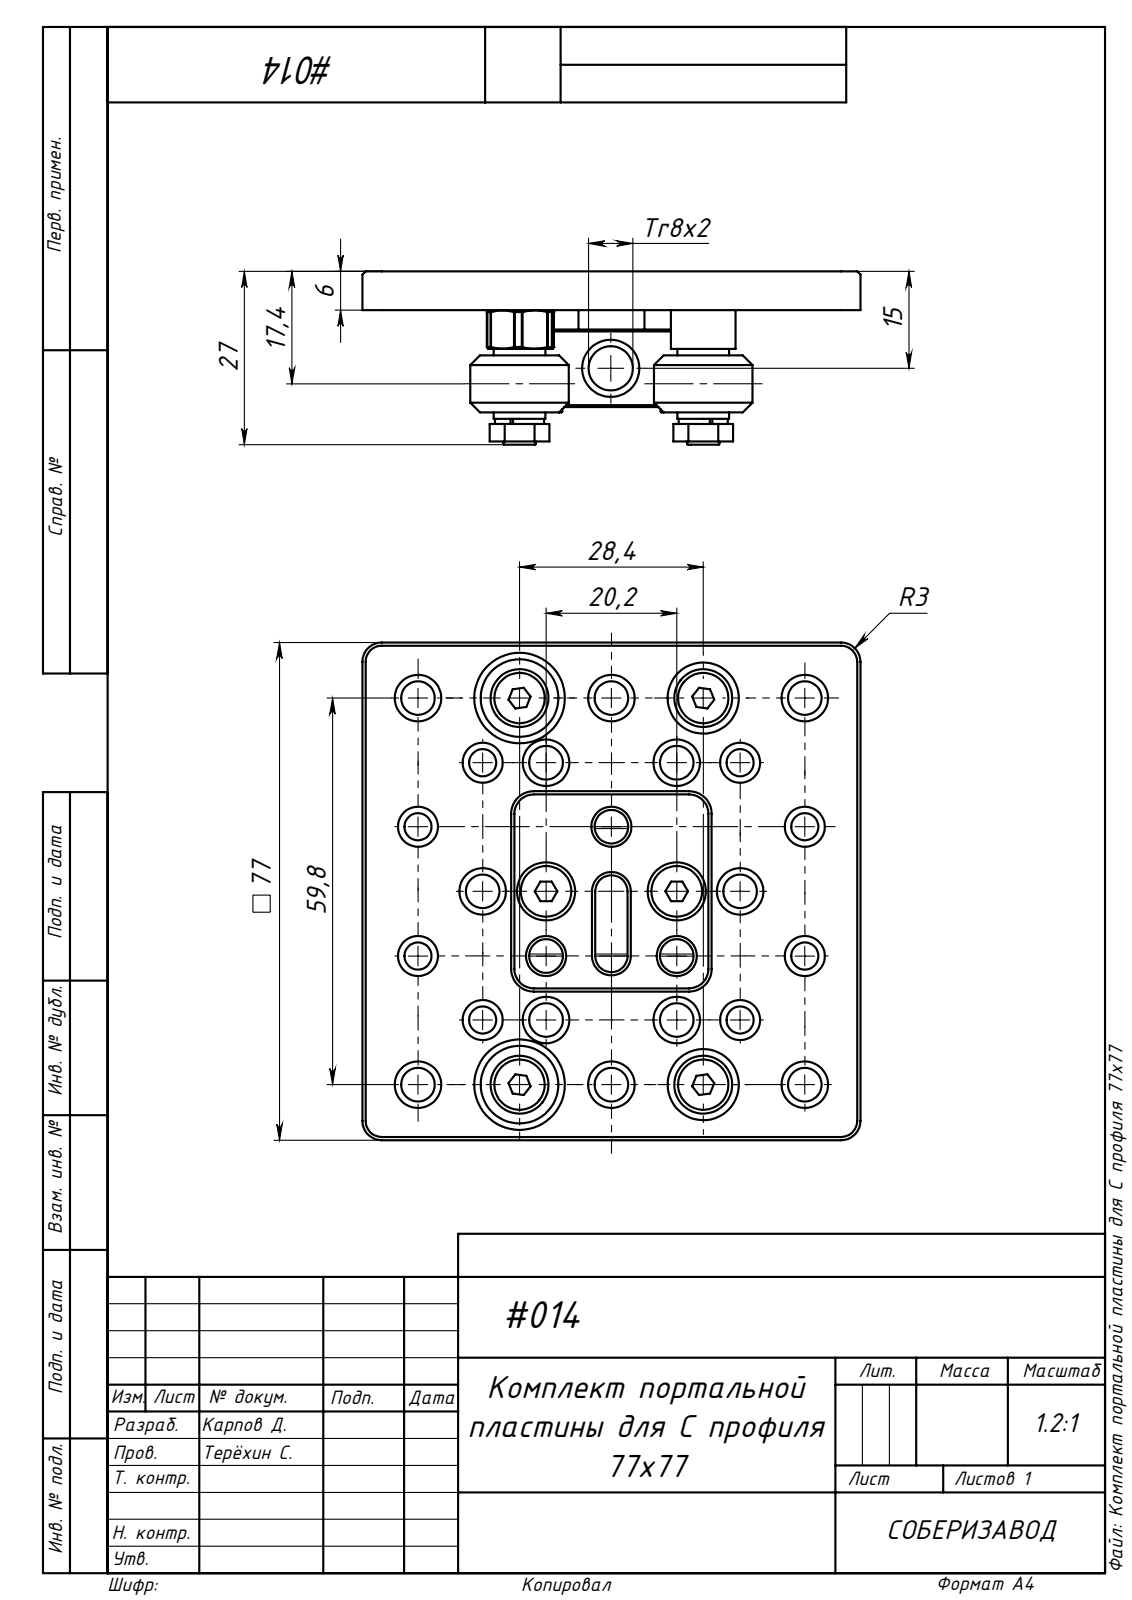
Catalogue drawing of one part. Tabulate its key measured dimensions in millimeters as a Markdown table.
| quantity | value |
| --- | --- |
| part name | A243 Пластина портальная 77х77 (С-профиля)_00; Комплект портальной пластины для С профиля 77x77; A199 Дистанционная втулка 5х3 мм; A178 Сборка ролика_00 (+7 more) |
| STEP written by | SolidWorks 2021 (AUTOMOTIVE_DESIGN) |
| units | millimeters |
| bodies | 80 solids, 1759 faces (391 planar, 510 cylindrical, 858 other) |
| overall size | 77 × 77 × 26.8 |
| volume | 46 548 mm³ |
| surface area | 35 001 mm² |
| round holes (diameter × count) | 5.2 × 19, 4.2 × 12, 5.15 × 6, 4.1 × 4, 5 × 4, 5.3 × 4, 6.09 × 4, 7.8 × 4, 8.4 × 4, 8.65 × 4, 4.13 × 2, 5.1 × 2 |
| round bosses / shafts (diameter × count) | 15.23 × 4, 10 × 4, 8.95 × 4, 8.64 × 4, 8 × 4, 7.6 × 4, 6.27 × 4, 6 × 4 |
| partial cylindrical surfaces (radius × count) | 0.2 × 28, 1 × 12, 3 × 8, 2.5 × 2 |
| main face-to-face distances | 6, 1.8, 4.2, 4, 3, 9, 1, 12, 5, 0.8 |
| hole center spacings | 22.18, 19.9, 35.92, 50.79, 14.14, 59.8, 22.27, 29.9 |
